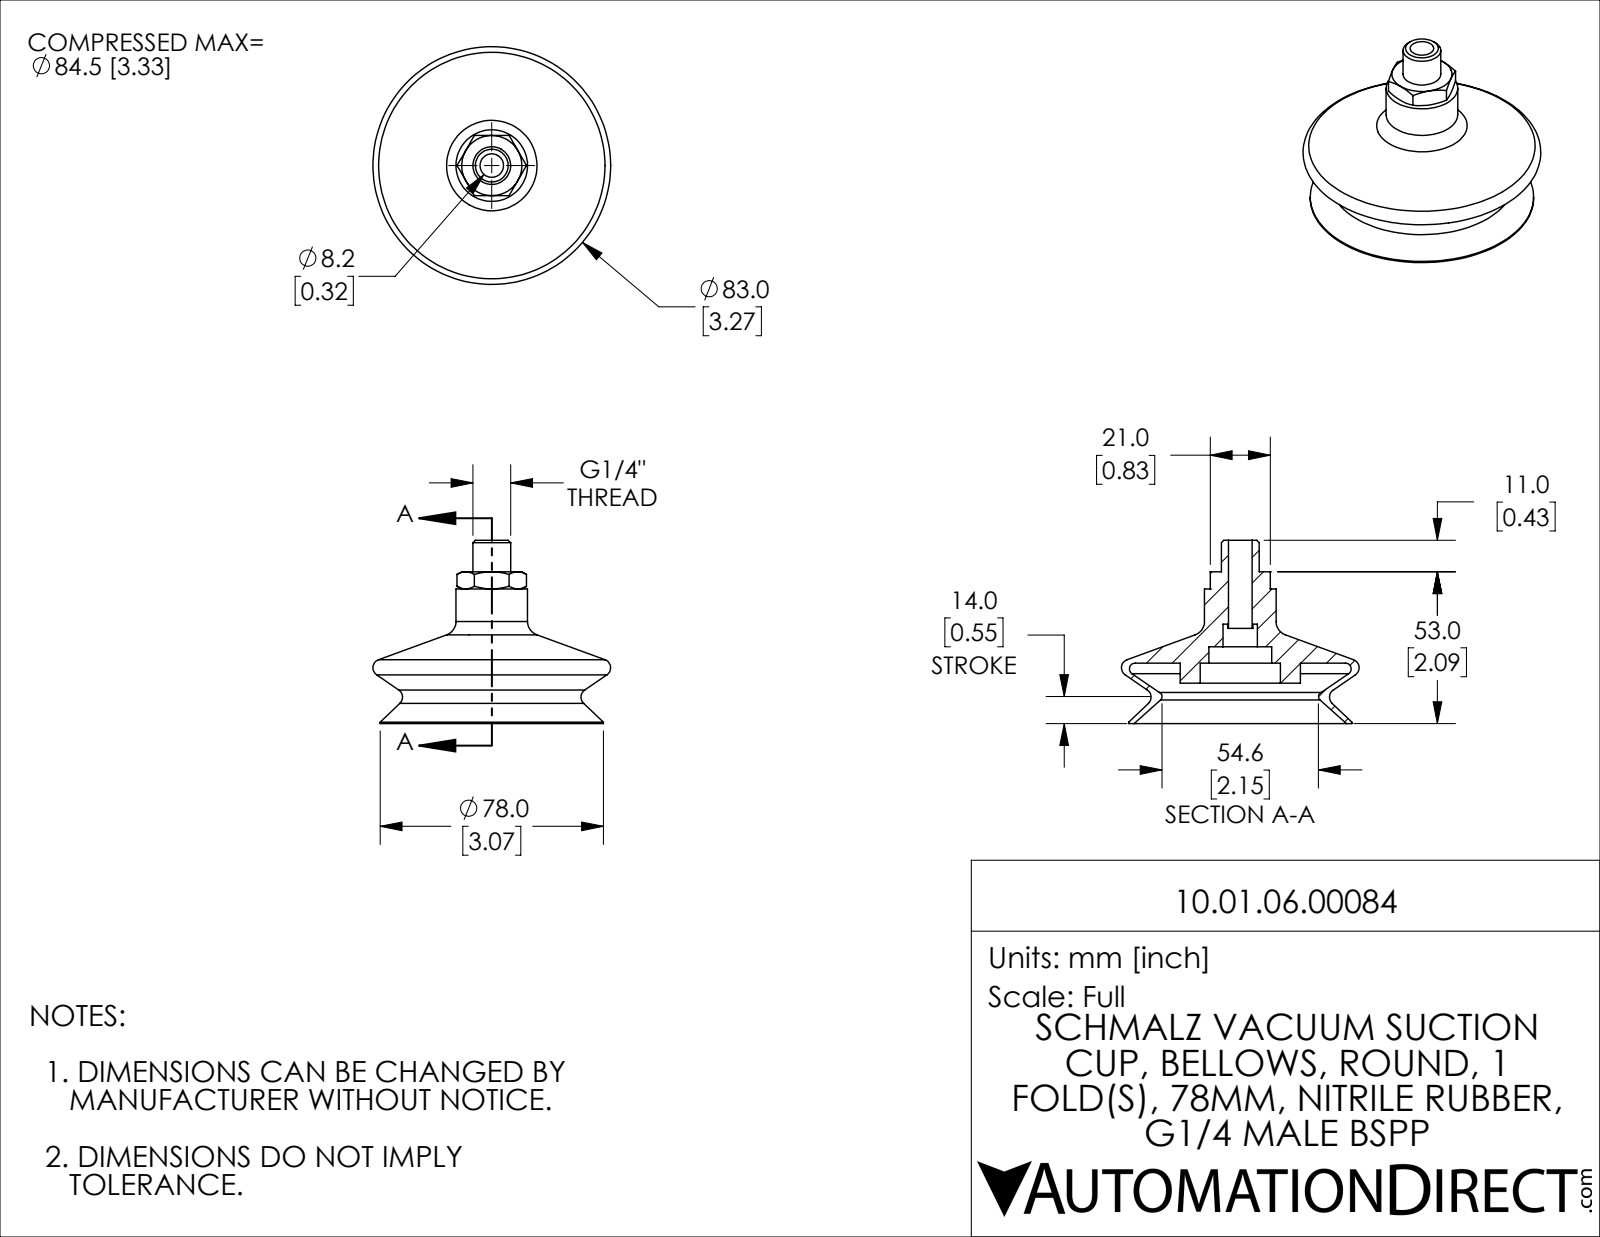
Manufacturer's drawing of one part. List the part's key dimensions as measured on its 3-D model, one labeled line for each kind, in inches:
Part name (STEP PRODUCT): 10.01.06.00084
STEP written by: SolidWorks 2021 (CONFIG_CONTROL_DESIGN)
Units: inches
Bodies: 1 solid, 64 faces (16 planar, 18 cylindrical, 30 other)
Overall size (bounding box): 3.268 × 3.268 × 2.52
Volume: 3.329 in³ · Surface area: 44.5 in²
Round holes (diameter × count): ⌀0.323 ×1, ⌀0.472 ×1, ⌀0.866 ×1, ⌀1.102 ×1
Round bosses / shafts (diameter × count): ⌀3.071 ×1, ⌀1.654 ×1, ⌀0.984 ×1, ⌀0.518 ×1, ⌀0.346 ×1
Main face-to-face distances: 0.276, 0.555, 0.831, 1.056, 0.501, 0.226, 2.087, 1.531, 1.256, 1.03
